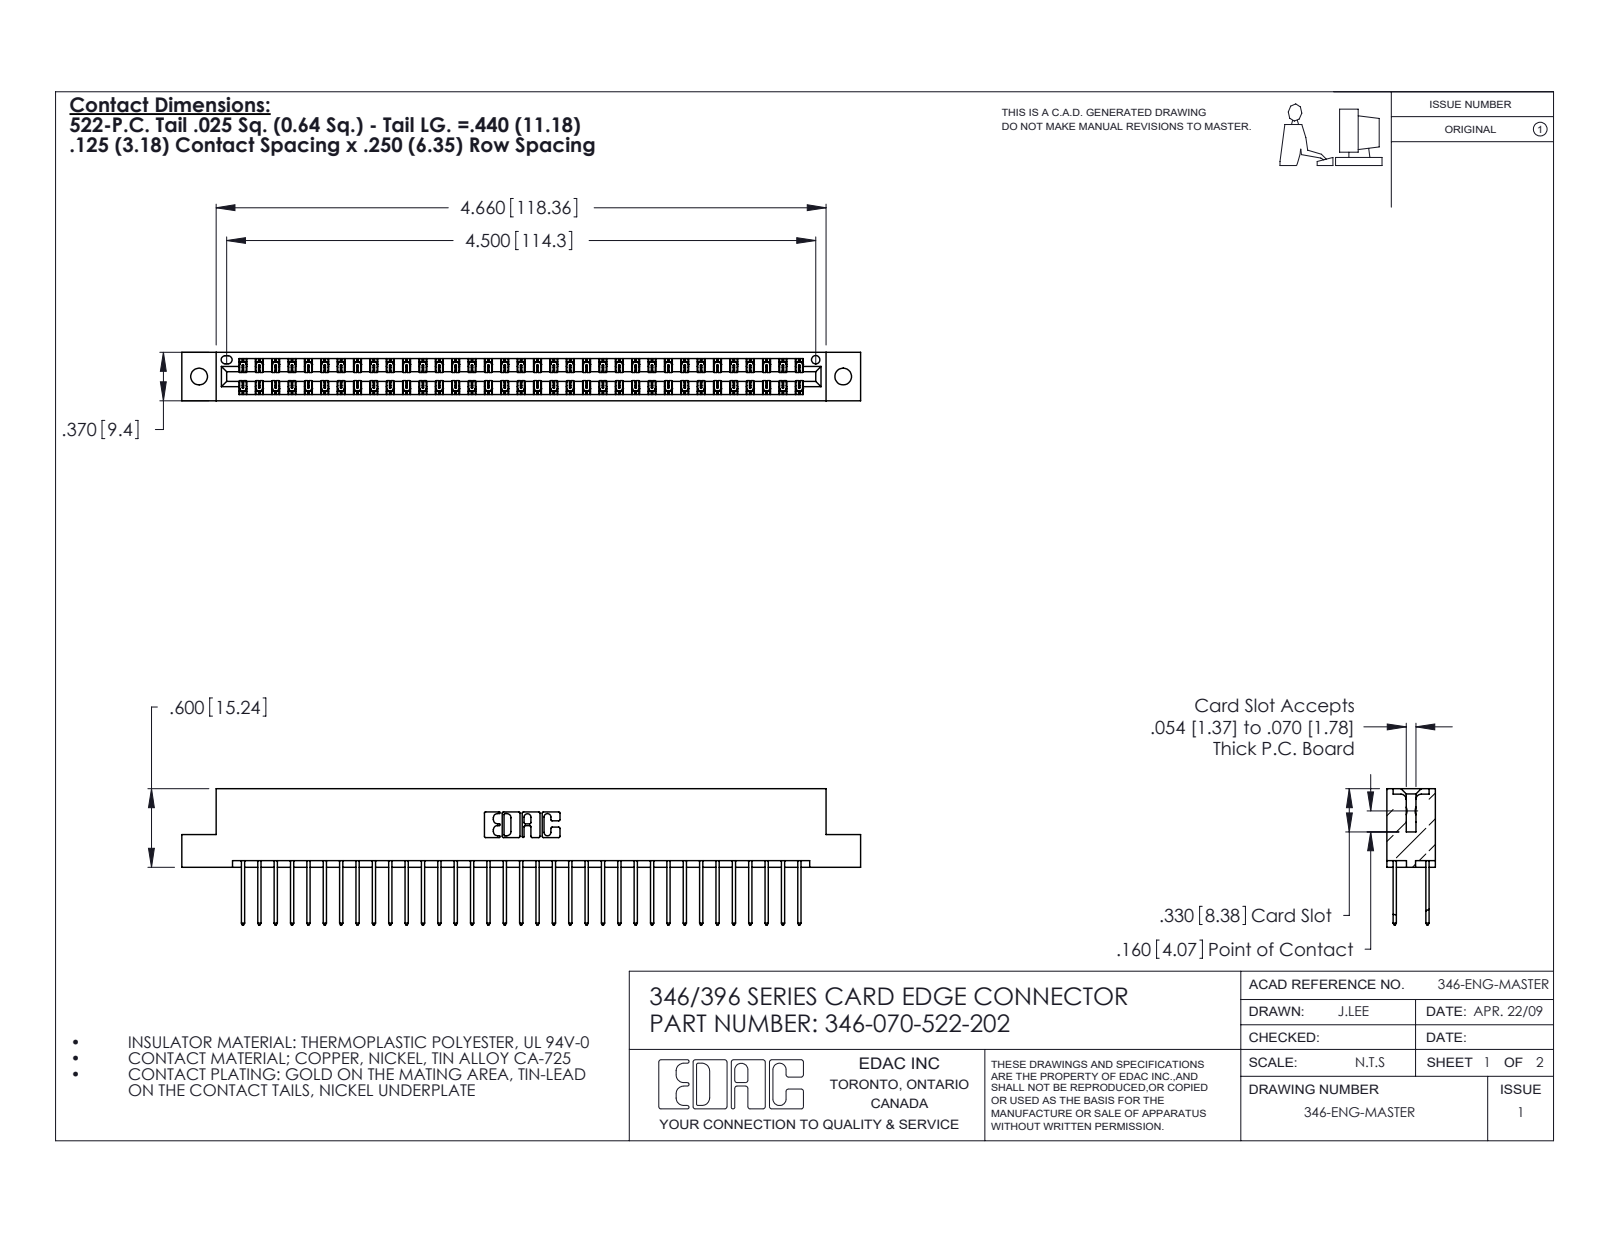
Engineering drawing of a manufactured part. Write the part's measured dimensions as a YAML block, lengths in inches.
part_name: "345-292-001_345-293-122; 346-070-522-202; 346 Part_Flush Mounting Lugs - 0.128 Dia"
step_written_by: "SolidWorks 2020 (CONFIG_CONTROL_DESIGN)"
units: inches
bodies: {solids: 71, faces: 3762, planar: 2526, cylindrical: 1236, other: 0}
overall_size: [5.185, 1.04, 0.37]
volume: 0.789
surface_area: 28.25
round_holes:
  - {diameter: 0.128, count: 2}
  - {diameter: 0.064, count: 1}
partial_cylinders:
  - {radius: 0.006, count: 105}
  - {radius: 0.01, count: 70}
  - {radius: 0.01, count: 22}
  - {radius: 0.007, count: 6}
  - {radius: 0.031, count: 6}
  - {radius: 0.026, count: 3}
  - {radius: 0.014, count: 2}
  - {radius: 0.022, count: 2}
face_to_face_distances: [0.048, 0.322, 0.25, 0.37, 0.072, 0.298, 0.025, 0.275, 0.148, 0.222]
hole_center_spacings: [0.246, 4.711, 4.92]
